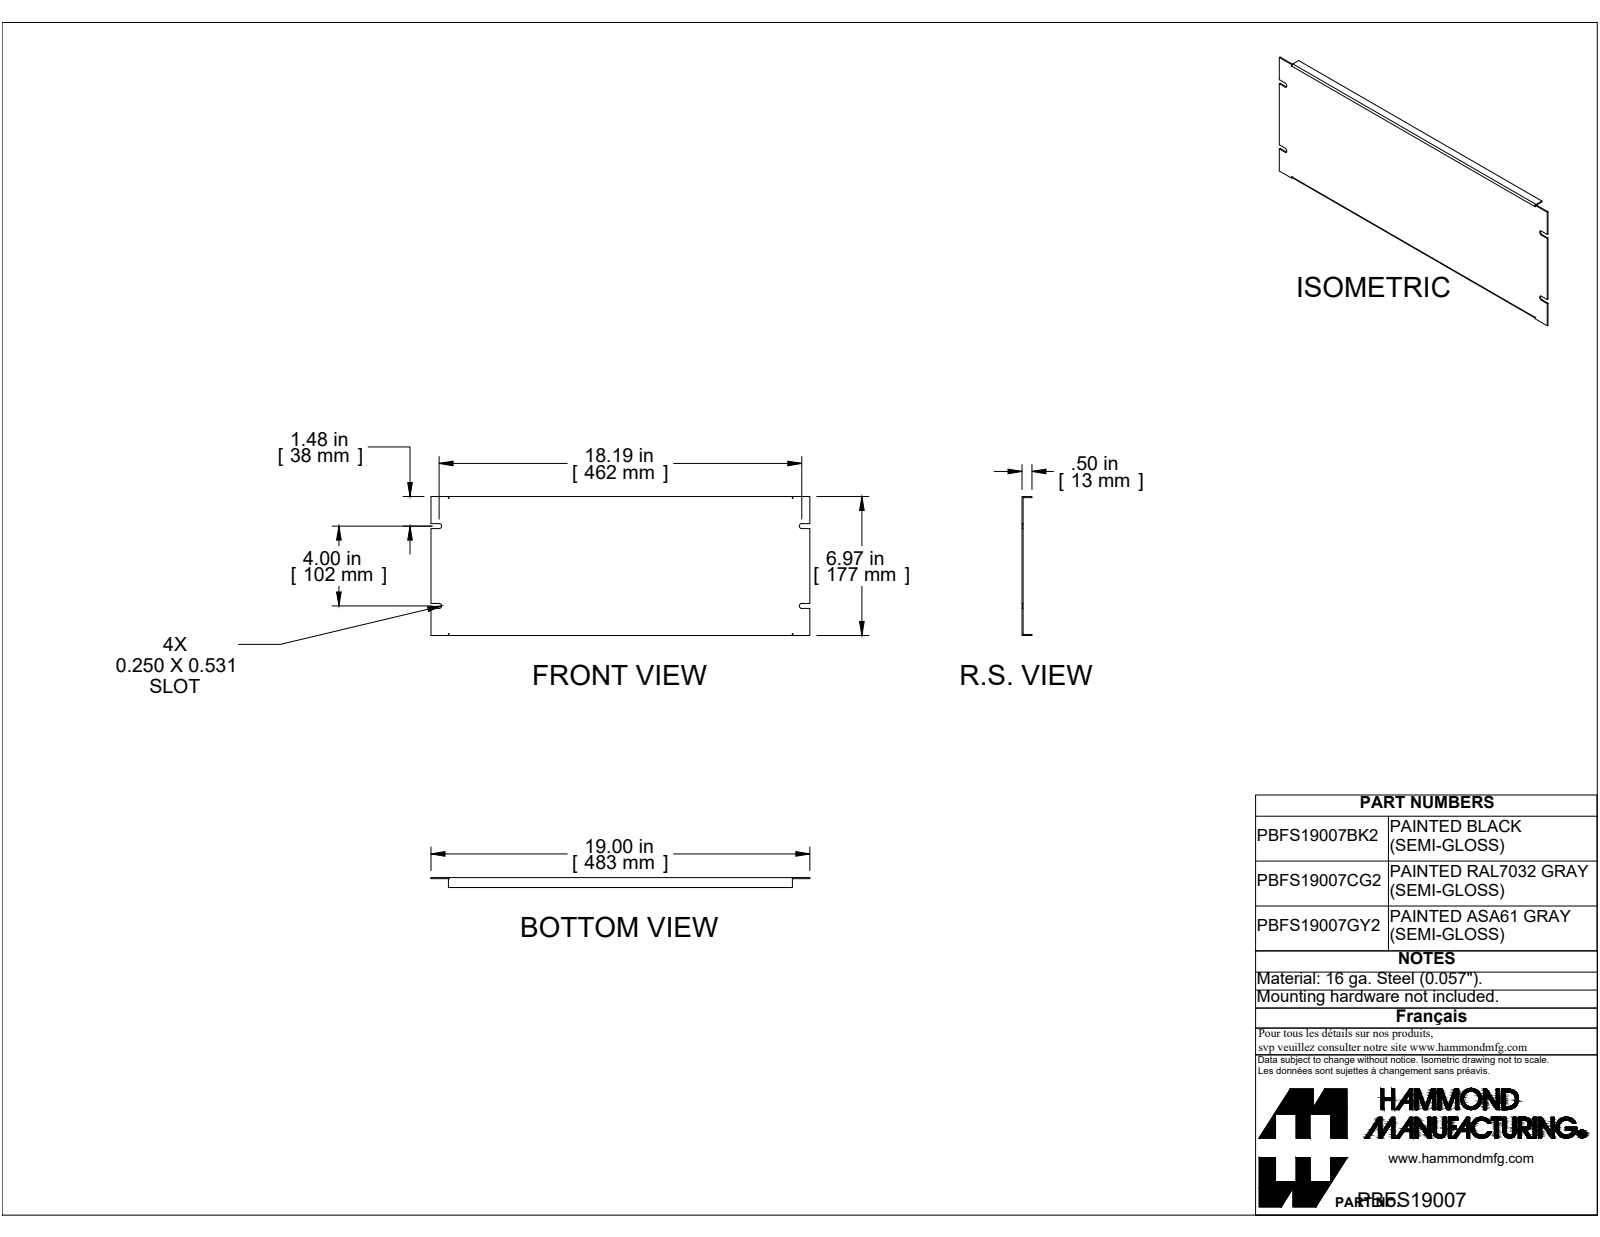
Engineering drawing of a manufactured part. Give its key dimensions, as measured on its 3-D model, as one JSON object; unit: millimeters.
{"part_name": "PBFS19007", "step_written_by": "SolidWorks 2019 (CONFIG_CONTROL_DESIGN)", "units": "millimeters", "bodies": {"solids": 1, "faces": 46, "planar": 38, "cylindrical": 8, "other": 0}, "overall_size": [482.6, 177, 12.7], "volume_mm3": 136700, "surface_area_mm2": 191000, "partial_cylinders_radius": [[3.2, 4], [0.7, 2], [2.2, 2]], "face_to_face_distances": [1.4, 1.4, 175.5, 177, 174.1, 12.7, 11.3, 482.6, 22.2, 460.4]}
